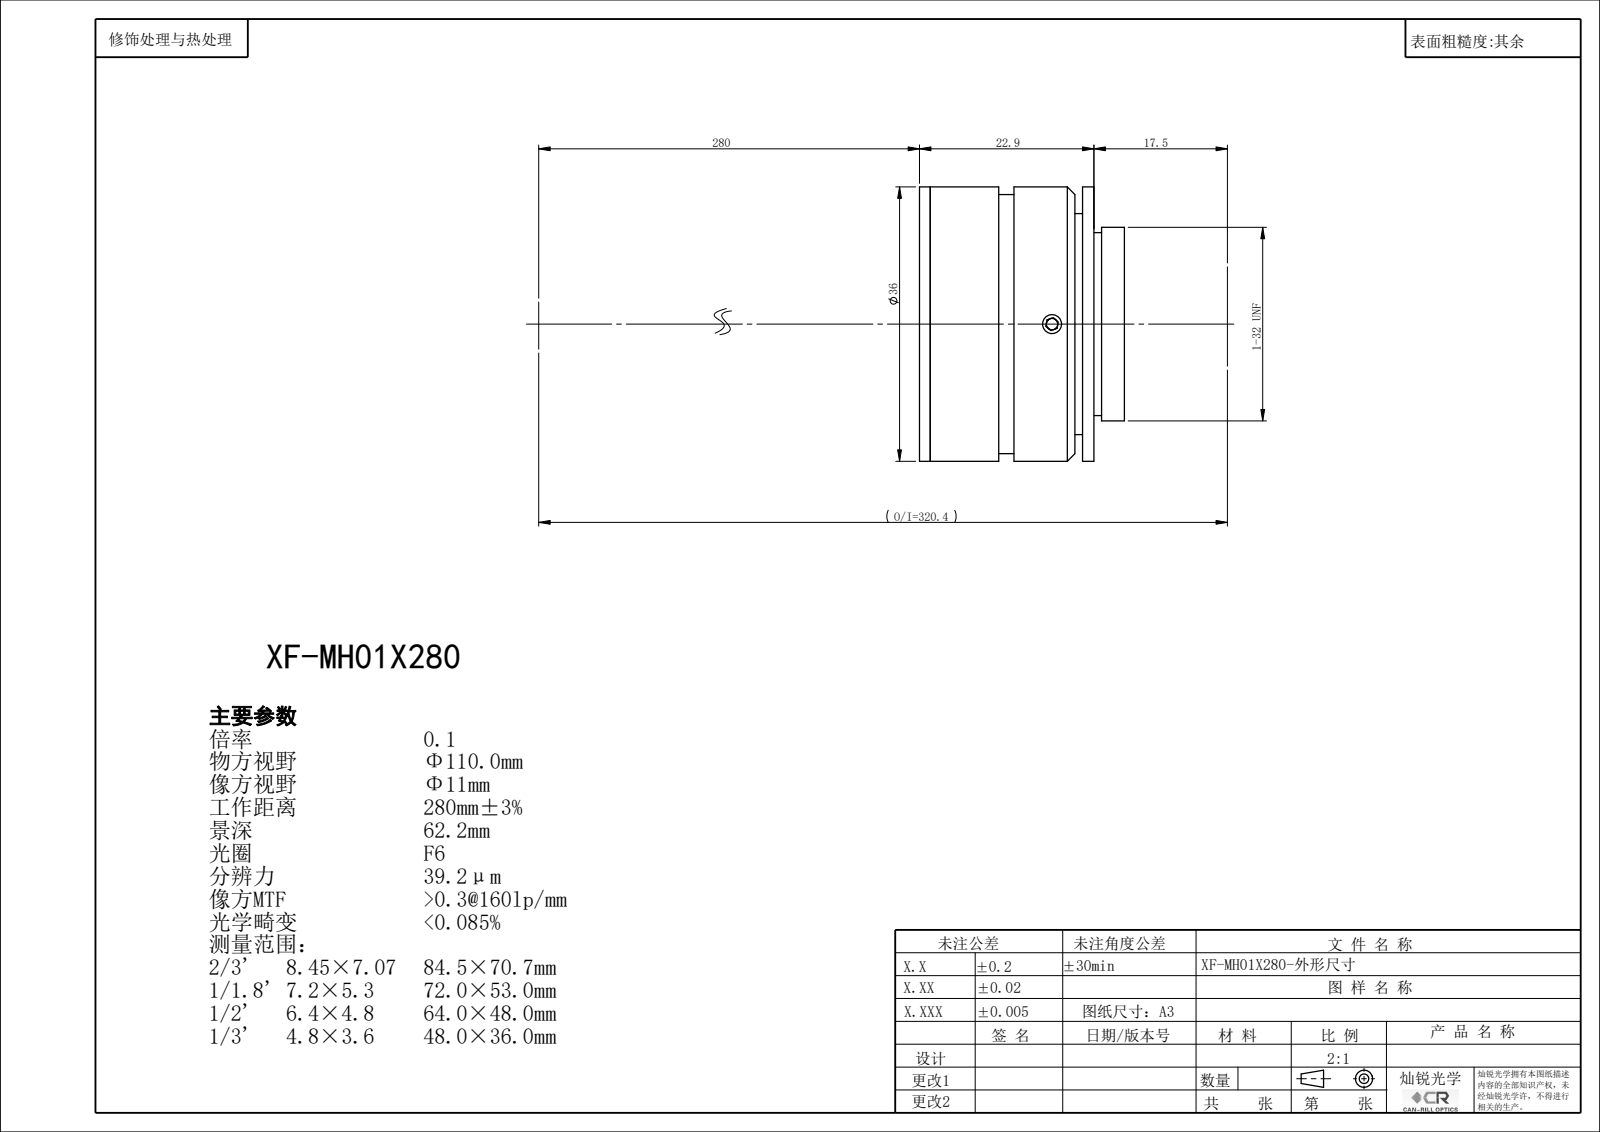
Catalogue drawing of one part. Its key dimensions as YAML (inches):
part_name: "XF-MH01X280"
step_written_by: "SolidWorks 2022 (CONFIG_CONTROL_DESIGN)"
units: inches
bodies: {solids: 0, faces: 95, planar: 45, cylindrical: 38, other: 12}
overall_size: [1.417, 1.417, 1.059]
round_holes:
  - {diameter: 0.098, count: 3}
  - {diameter: 0.315, count: 1}
  - {diameter: 0.354, count: 1}
  - {diameter: 0.409, count: 1}
  - {diameter: 0.512, count: 1}
  - {diameter: 0.669, count: 1}
  - {diameter: 0.827, count: 1}
  - {diameter: 0.846, count: 1}
  - {diameter: 0.98, count: 1}
  - {diameter: 1.024, count: 1}
round_bosses_or_shafts:
  - {diameter: 1.417, count: 1}
  - {diameter: 1.339, count: 1}
  - {diameter: 1, count: 1}
  - {diameter: 0.945, count: 1}
face_to_face_distances: [0.079, 0.846, 0.039, 0.055, 0.902, 0.803, 0.843, 0.059, 0.787, 0.177]
